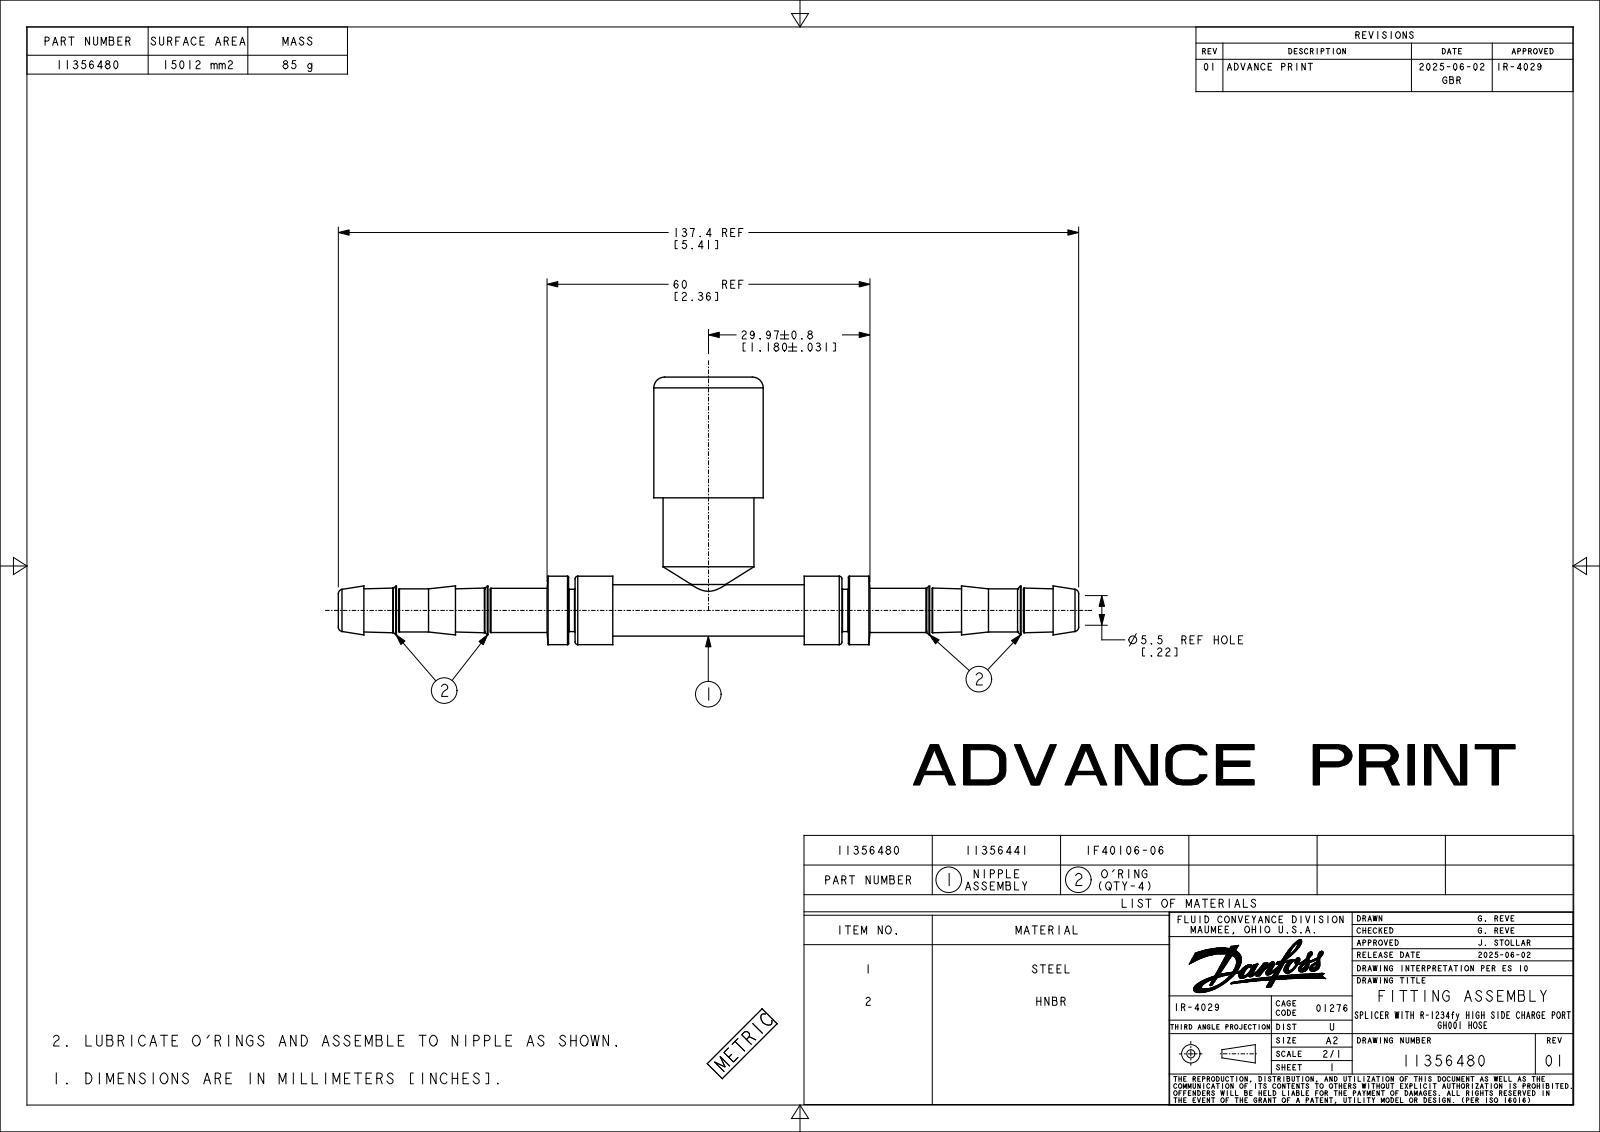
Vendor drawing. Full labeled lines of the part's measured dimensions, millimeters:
Part name (STEP PRODUCT): 11356441_TUBE; FW1172-0606; FF4398-02; FF90192-02 (+7 more)
STEP written by: CREO PARAMETRIC BY PTC INC, 2022124 (CONFIG_CONTROL_DESIGN)
Units: millimetres
Bodies: 10 solids, 191 faces (37 planar, 80 cylindrical, 74 other)
Overall size (bounding box): 137.4 × 49.6 × 20.3
Volume: 13 600 mm³ · Surface area: 15 250 mm²
Round holes (diameter × count): ⌀4.7 ×1, ⌀5.5 ×1, ⌀6.4 ×1, ⌀6.6 ×1, ⌀7.7 ×1, ⌀9.2 ×1, ⌀9.6 ×1, ⌀10 ×1, ⌀10.5 ×1, ⌀16 ×1
Round bosses / shafts (diameter × count): ⌀20.3 ×1, ⌀16.9 ×1, ⌀16.9 ×1, ⌀14.9 ×1, ⌀12.9 ×1, ⌀12.7 ×1, ⌀10 ×1, ⌀9.5 ×1
Main face-to-face distances: 1.9, 4.2, 47.8, 20.5, 22.4, 1.2, 50.7, 3, 46.5, 8.2
